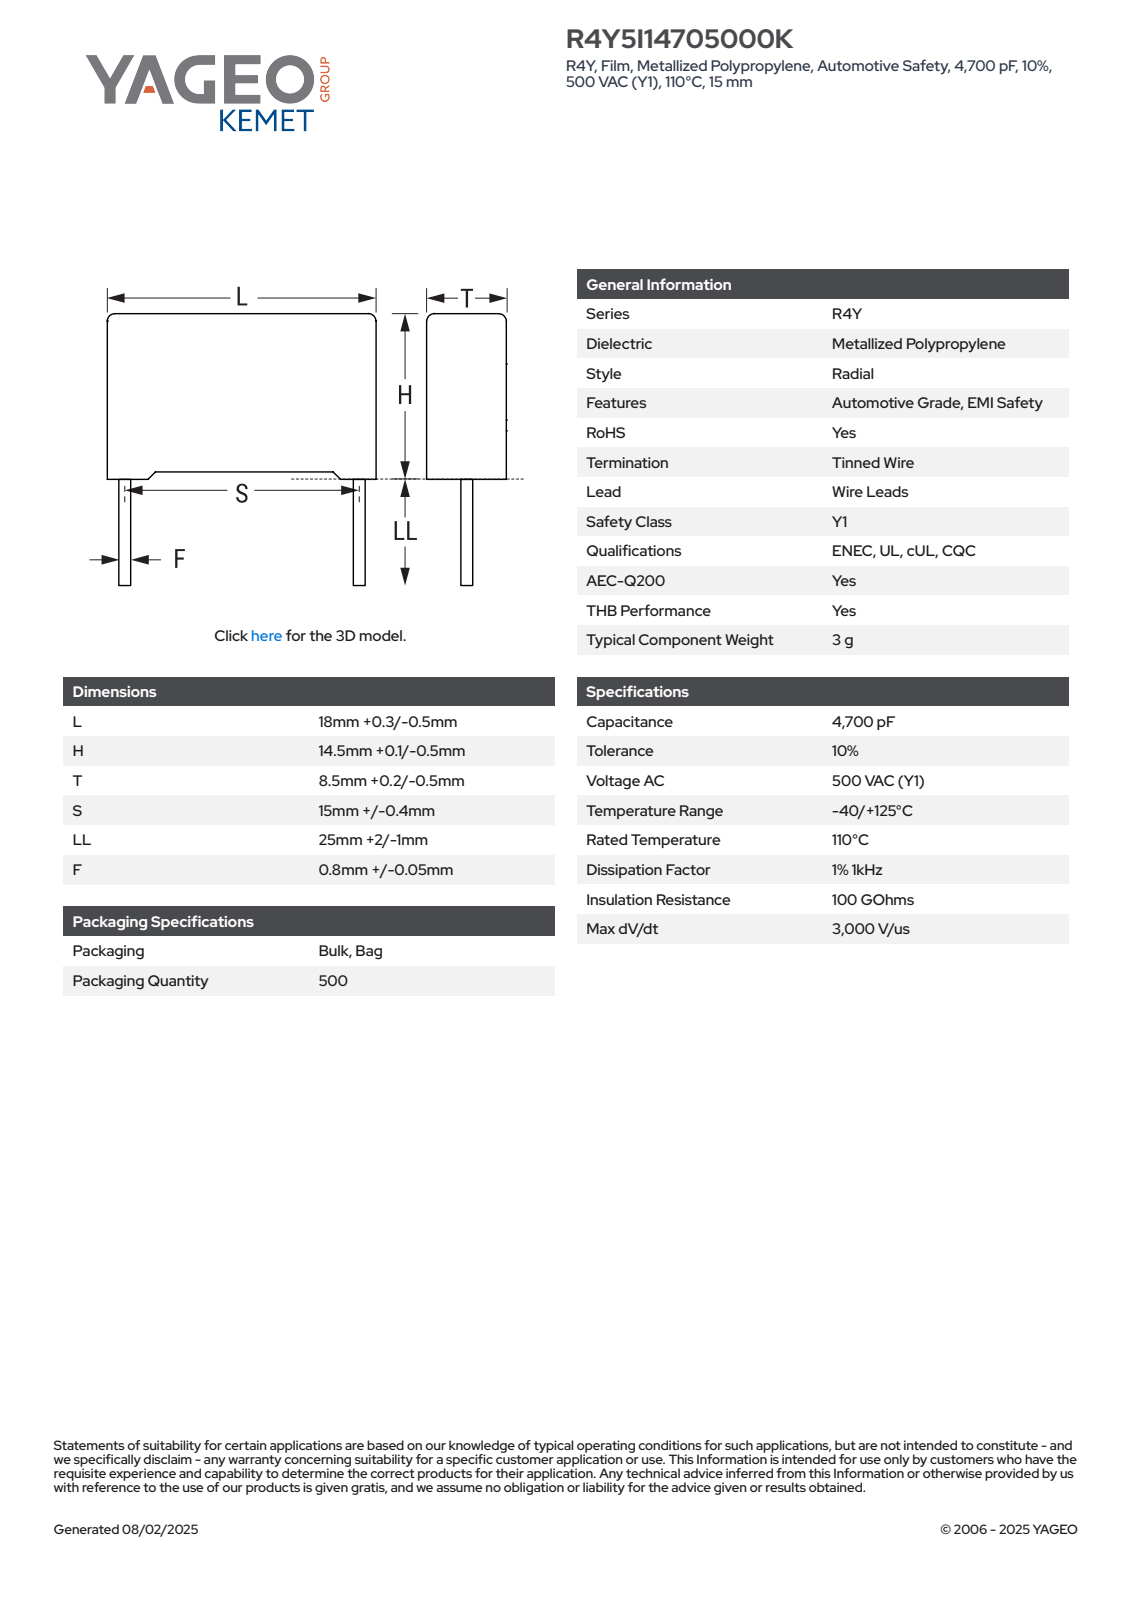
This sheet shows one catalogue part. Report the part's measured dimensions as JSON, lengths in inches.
{"part_name": "CFR_RB2_18X14.5X8.5_L18.3H14.6T8.7S15LL27F0.85", "step_written_by": "SolidWorks 2021 (AUTOMOTIVE_DESIGN)", "units": "inches", "bodies": {"solids": 4, "faces": 85, "planar": 77, "cylindrical": 8, "other": 0}, "overall_size": [1.638, 0.72, 0.343], "volume_in3": 0.137, "surface_area_in2": 1.989, "round_bosses_or_shafts": [[0.033, 2]], "partial_cylinders_radius": [[0.02, 4]], "face_to_face_distances": [0.343, 0.545, 0.72, 0.024, 0.03, 0.575, 0.319, 0.02, 0.555, 0.696]}
